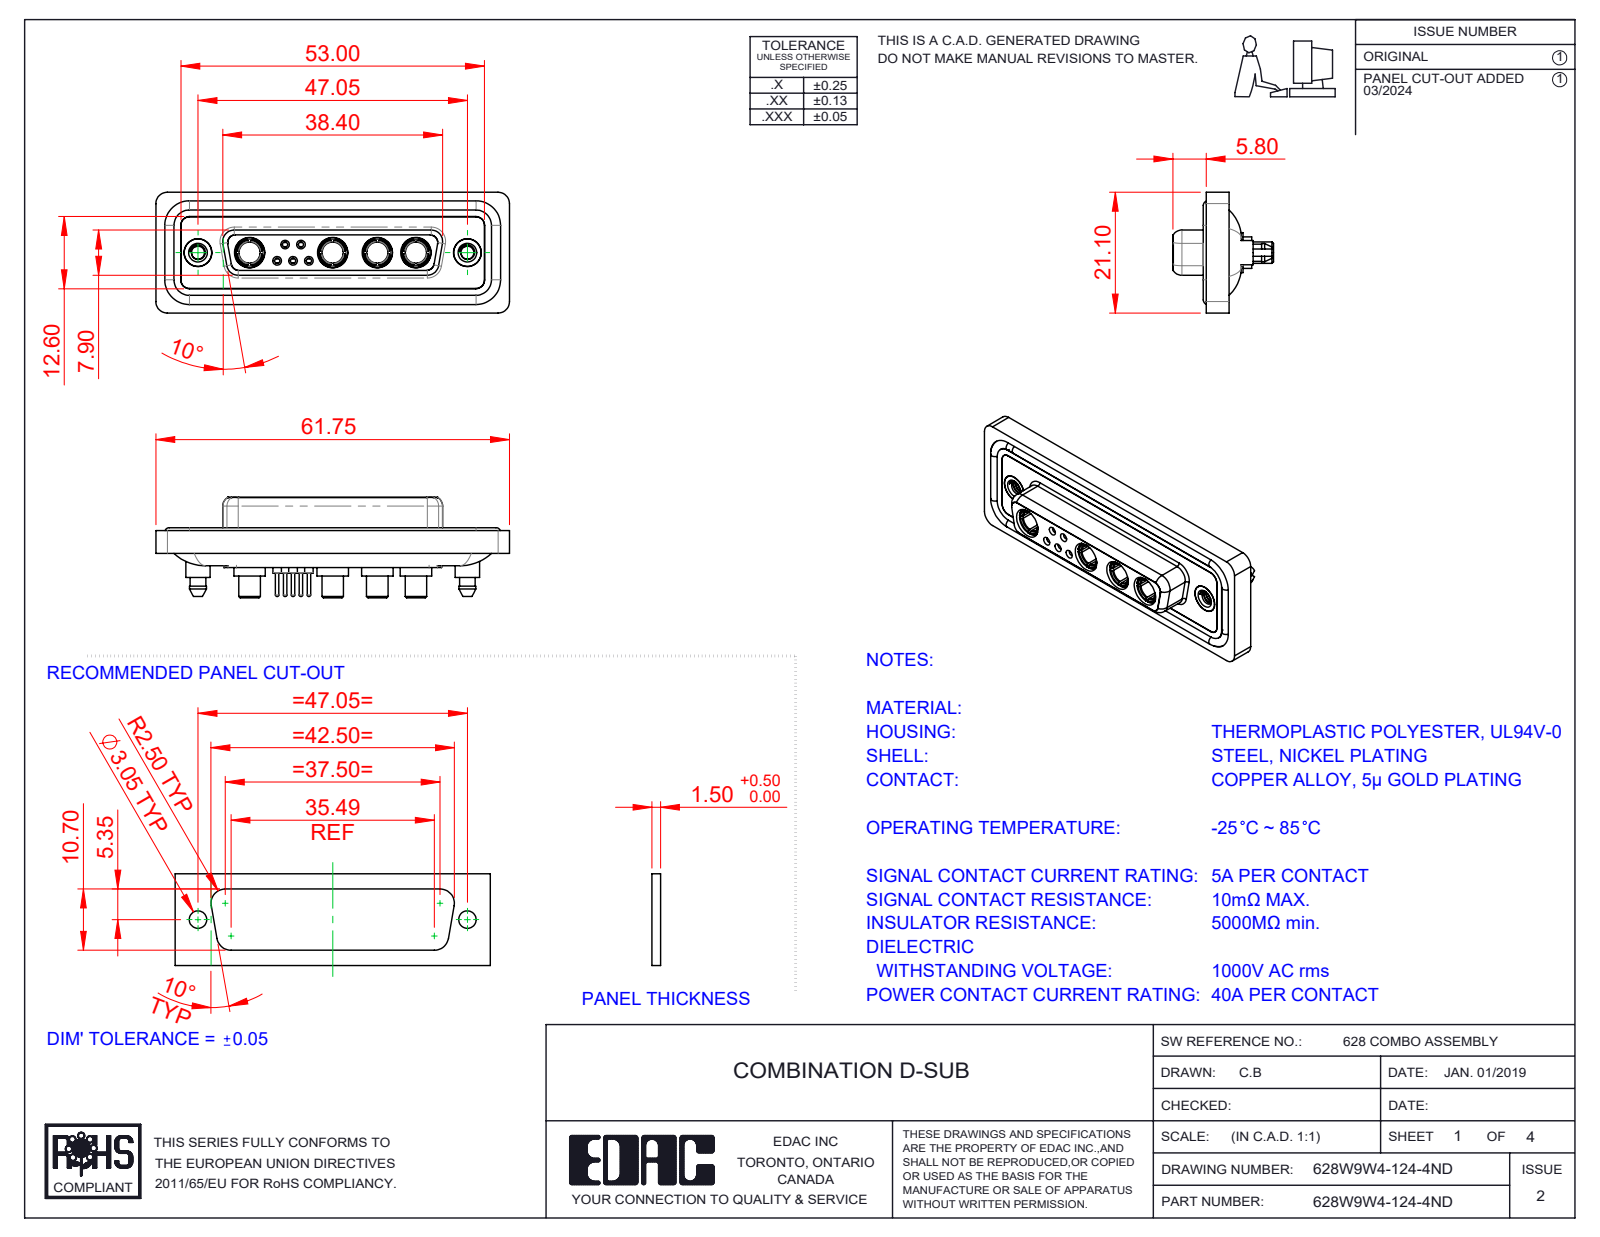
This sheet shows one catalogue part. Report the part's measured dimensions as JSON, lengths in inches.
{"part_name": "628Combo Housing_9W4; 628W9W4-124-4ND; 628Combo Threaded Boardlock_D; 628Combo Shell Front_25 Contacts (+5 more)", "step_written_by": "SolidWorks 2023 (CONFIG_CONTROL_DESIGN)", "units": "inches", "bodies": {"solids": 20, "faces": 1023, "planar": 312, "cylindrical": 423, "other": 288}, "overall_size": [2.431, 0.831, 0.691], "volume_in3": 0.515, "surface_area_in2": 21.61, "round_holes": [[0.191, 6], [0.035, 5], [0.043, 5], [0.059, 5], [0.079, 5], [0.146, 4], [0.209, 4], [0.063, 3], [0.067, 2], [0.089, 2], [0.157, 2], [0.159, 2]], "round_bosses_or_shafts": [[0.063, 6], [0.087, 5], [0.024, 5], [0.217, 4], [0.205, 4], [0.195, 4], [0.187, 4], [0.148, 4]], "partial_cylinders_radius": [[0.059, 24], [0.079, 18], [0.063, 10], [0.053, 8], [0.01, 4], [0.02, 4], [0.024, 4], [0.026, 4]], "face_to_face_distances": [0.016, 0.071, 0.293, 0.222, 0.02, 0.278, 0.26, 0.063, 0.043, 0.114], "hole_center_spacings": [0.124, 0.109, 0.198, 0.109, 0.173, 0.198, 0.218, 0.226]}
